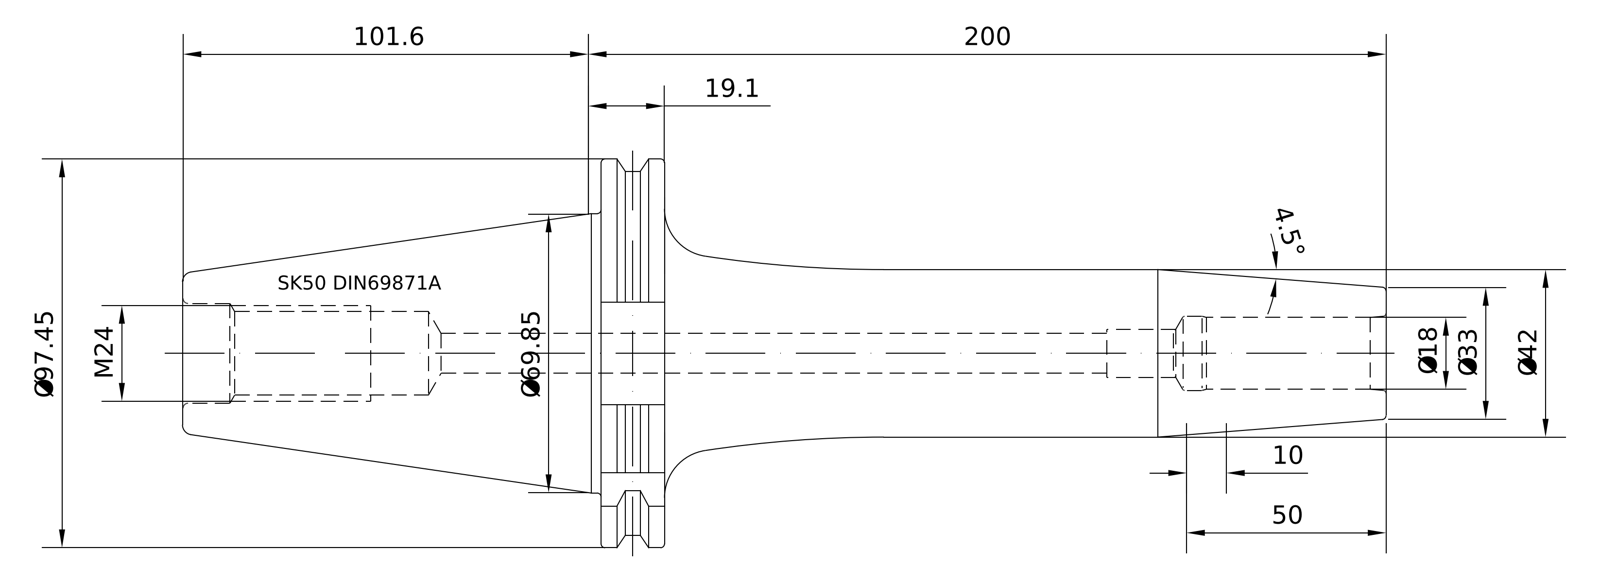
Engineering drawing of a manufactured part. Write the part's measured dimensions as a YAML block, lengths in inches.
part_name: "50-446-18"
step_written_by: "PRO/ENGINEER BY PARAMETRIC TECHNOLOGY CORPORATION, 2010430 (CONFIG_CONTROL_DESIGN)"
units: inches
bodies: {solids: 1, faces: 95, planar: 21, cylindrical: 24, other: 50}
overall_size: [11.874, 3.837, 3.701]
volume: 35.29
surface_area: 104.4
round_holes:
  - {diameter: 0.709, count: 1}
  - {diameter: 0.817, count: 1}
  - {diameter: 0.985, count: 1}
  - {diameter: 1.012, count: 1}
round_bosses_or_shafts:
  - {diameter: 3.583, count: 1}
  - {diameter: 2.722, count: 1}
  - {diameter: 1.654, count: 1}
  - {diameter: 0.945, count: 1}
partial_cylinders:
  - {radius: 0.069, count: 1}
  - {radius: 1.919, count: 1}
face_to_face_distances: [0.624, 7.748, 7.124, 2.866, 4.126, 4.75, 11.874, 1.016, 9.906, 5.78]
